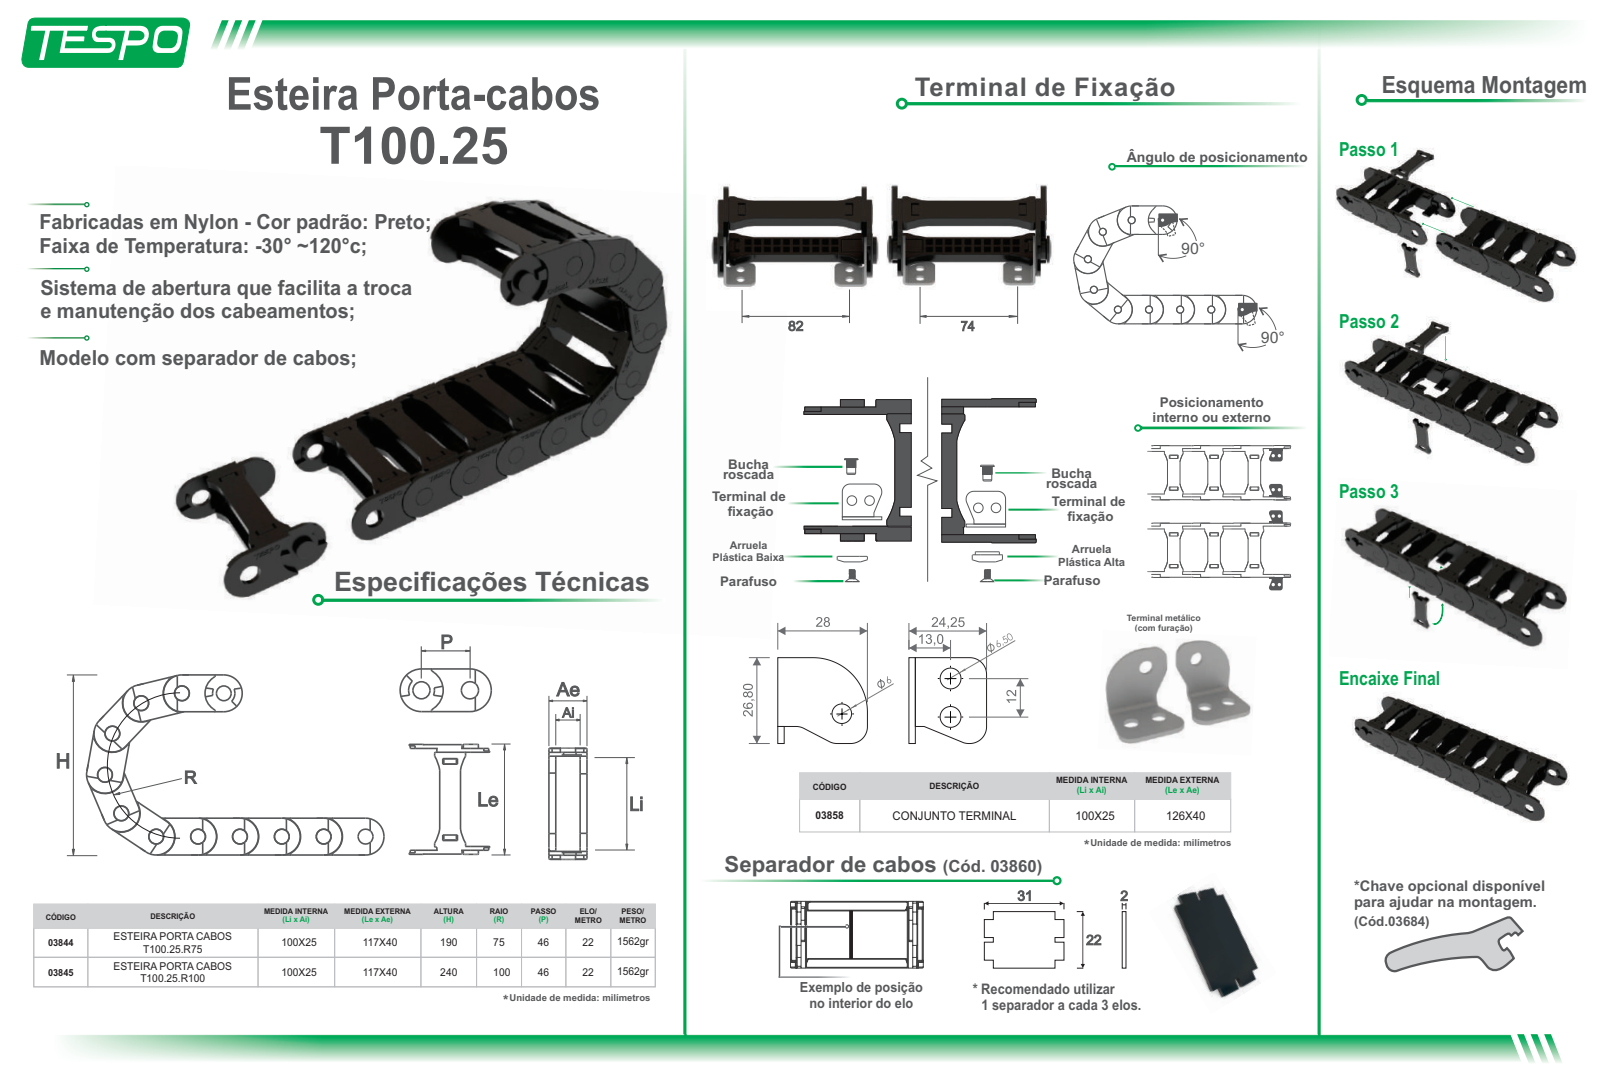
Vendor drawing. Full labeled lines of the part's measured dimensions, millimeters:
STEP written by: ST-DEVELOPER v15 (AUTOMOTIVE_DESIGN)
Units: millimetres
Bodies: 4 solids, 155 faces (92 planar, 0 cylindrical, 63 other)
Overall size (bounding box): 116.78 × 85.5 × 40
Volume: 62 937 mm³ · Surface area: 31 577 mm²
Main face-to-face distances: 4.05, 108.08, 7.2, 32.8, 104.03, 8.1, 112.13, 40, 25.6, 99.98
